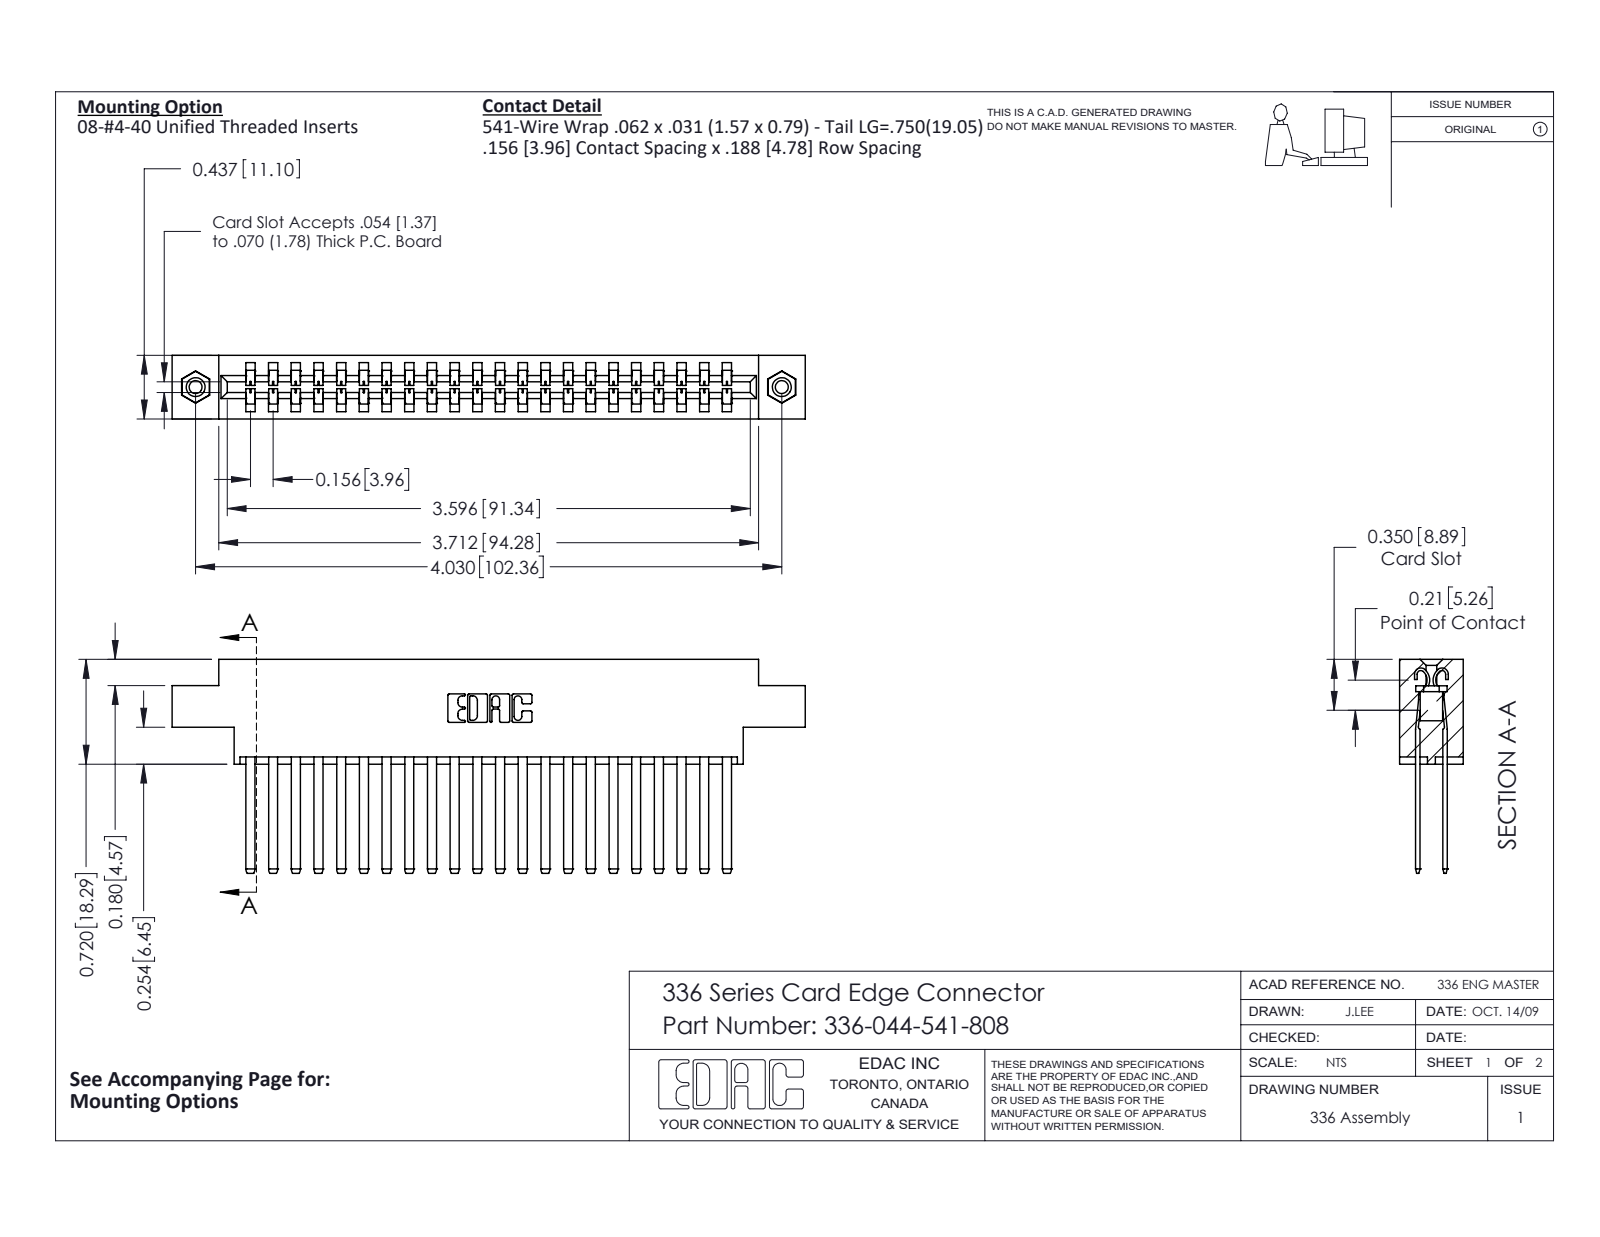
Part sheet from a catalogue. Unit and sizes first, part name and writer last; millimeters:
Units: millimetres
Overall size (bounding box): 110.6 × 37.3 × 11.1
Round holes (diameter × count): ⌀2.3 ×2, ⌀3.2 ×2, ⌀4 ×2
Round bosses / shafts (diameter × count): ⌀3.9 ×2
Partial cylindrical surfaces — rounded edges, fillets, slot ends (radius × count): R0.1 ×88, R1.4 ×44, R0.3 ×22, R0.2 ×6, R0.8 ×6, R0.6 ×4, R1 ×4, R0.7 ×3
Main face-to-face distances: 4.8, 8.3, 3.6, 7.5, 2.8, 0.8, 11.1, 0.8, 4, 4.6
Hole centre spacings: 102.4
Volume: 16 420 mm³ · Surface area: 20 690 mm²
Bodies: 47 solids, 2026 faces (1250 planar, 760 cylindrical, 16 other)
Part name (STEP PRODUCT): 336 Part_Offset - .156 Dia - TI; 336-044-541-808; 336-290-001_336-290-541; 345-250-001_345-250-003-102
STEP written by: SolidWorks 2020 (CONFIG_CONTROL_DESIGN)
